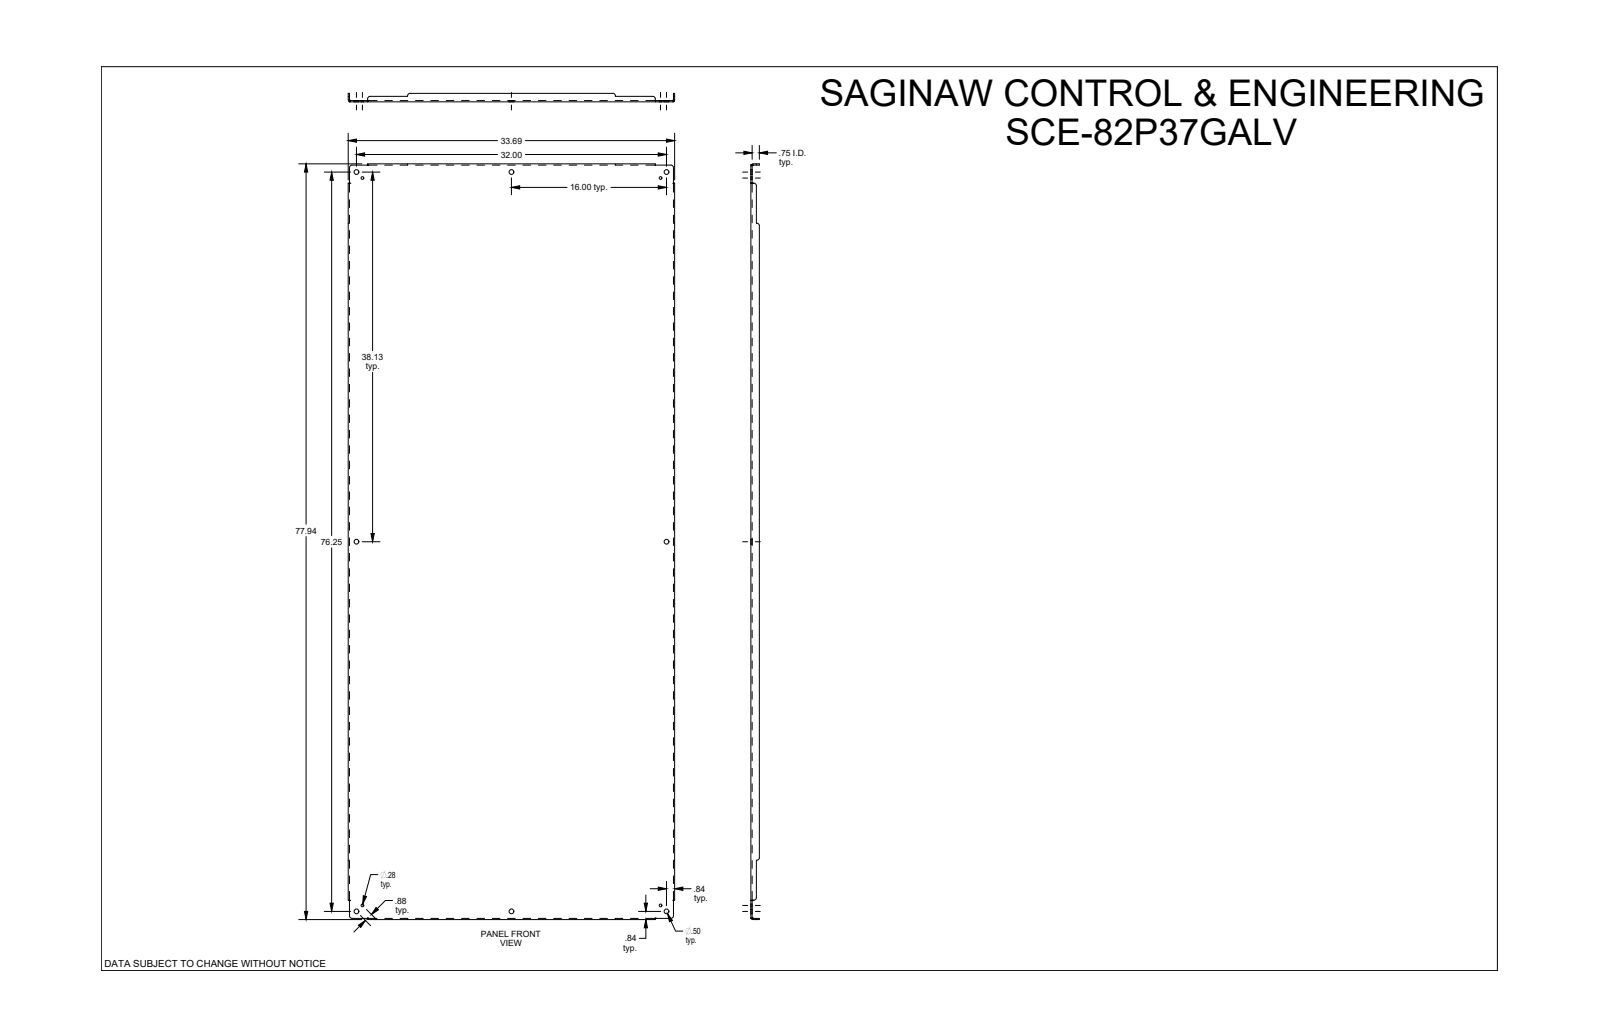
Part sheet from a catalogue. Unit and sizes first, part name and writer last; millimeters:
Units: millimetres
Overall size (bounding box): 1979.6 × 855.7 × 22.2
Round holes (diameter × count): ⌀12.7 ×8, ⌀7.1 ×4
Partial cylindrical surfaces — rounded edges, fillets, slot ends (radius × count): R6.4 ×12, R2.8 ×4, R6 ×4
Main face-to-face distances: 3.2, 852.5, 849.3, 855.6, 3.2, 1976.5, 19.1, 22.2, 1973.2, 1979.6
Hole centre spacings: 22.2, 391, 406.4, 797.2, 952.8, 968.4, 1050.2, 1242.1
Volume: 5 636 000 mm³ · Surface area: 3 570 000 mm²
Bodies: 1 solid, 110 faces (46 planar, 40 cylindrical, 24 other)
Part name (STEP PRODUCT): SCE-82P37GALV
STEP written by: SolidWorks 2019 (CONFIG_CONTROL_DESIGN)
